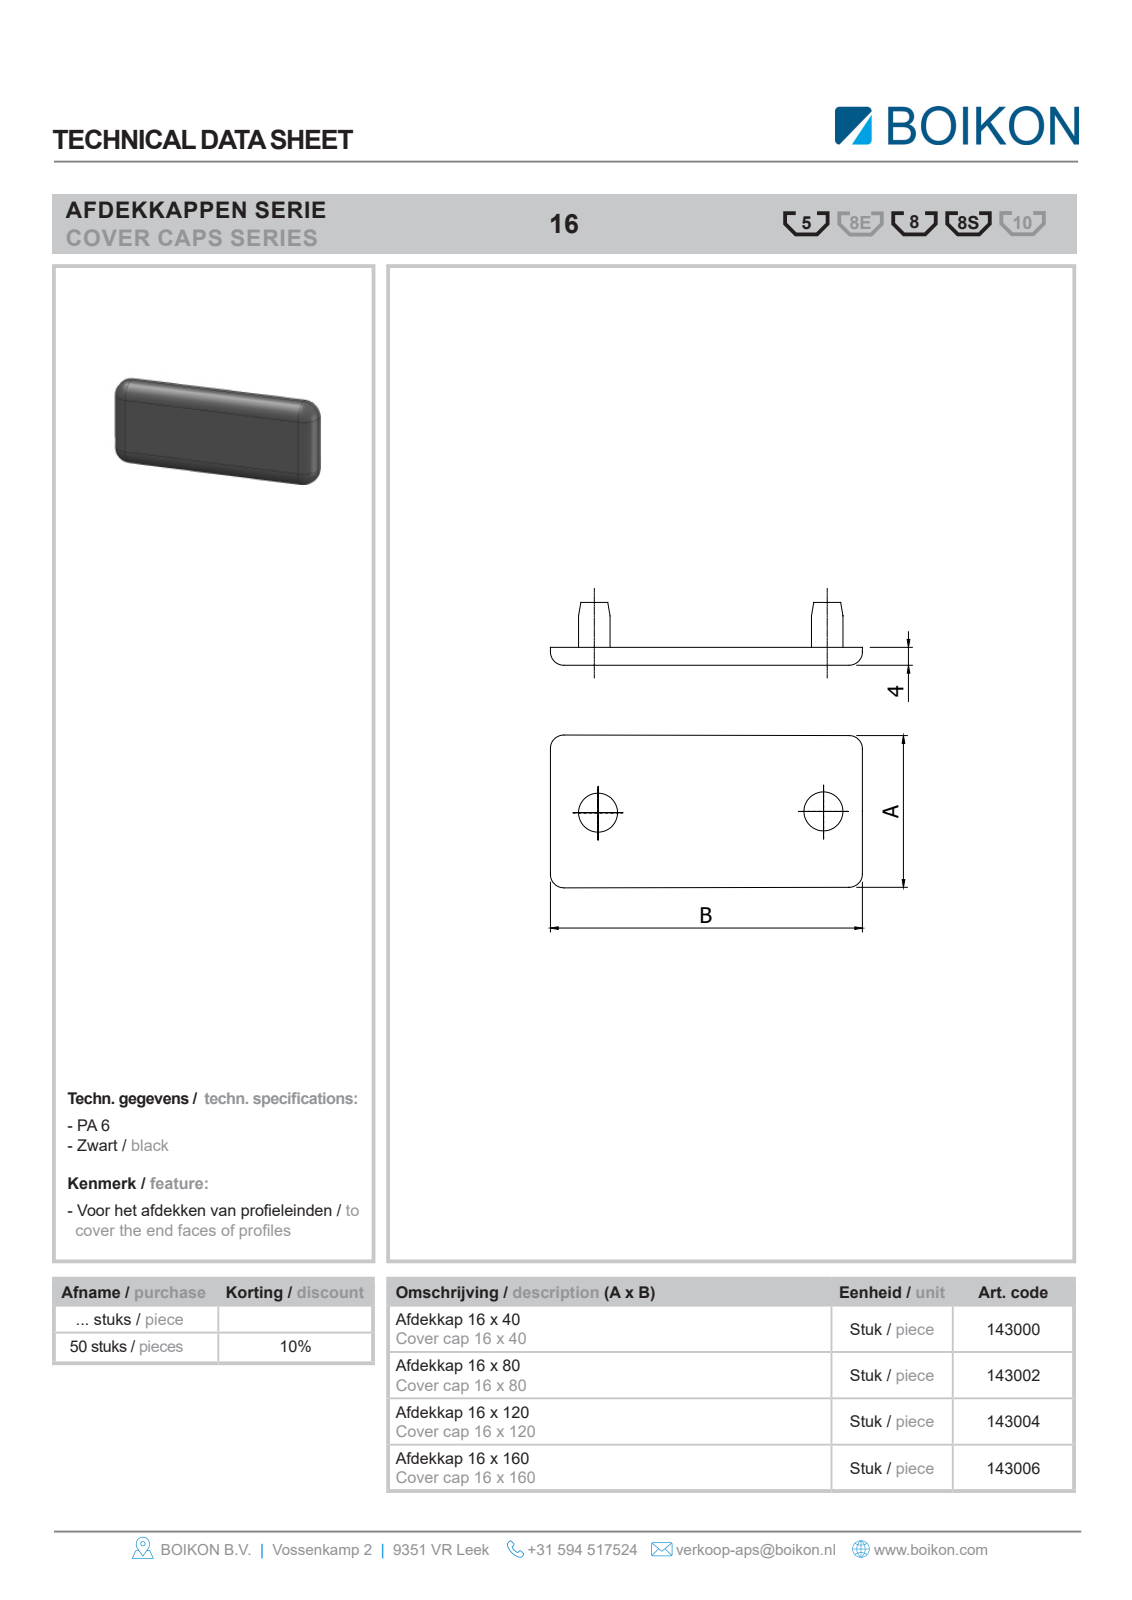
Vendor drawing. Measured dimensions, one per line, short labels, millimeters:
name: Root; 143000Afdekkap 16 x 40BOIKON
written by: HiCAD 2013 1802.4 Build 509 (AUTOMOTIVE_DESIGN)
unit: mm
bodies: 1 solid, 18 faces (6 planar, 8 cylindrical, 4 other)
size: 40 × 16 × 4
volume: 2 331 mm³; area: 1 550 mm²
rounds: 8× R3
face distances: 4, 16, 40
